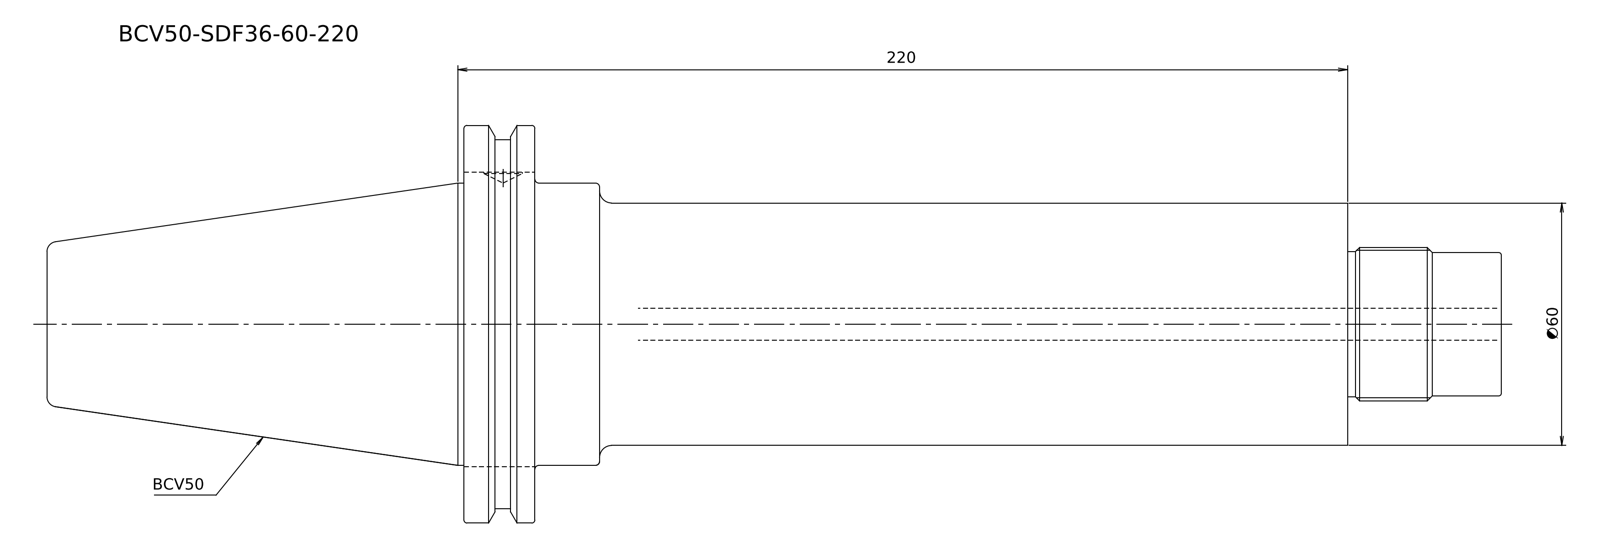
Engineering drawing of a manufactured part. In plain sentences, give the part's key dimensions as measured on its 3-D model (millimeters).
Its 3-D file was written by "Kubotek KeyCreator 2011 V10.0.2 (22737) (automotive_design)". It is 1 solid with 17 faces: 7 planar, 6 cylindrical and 4 other. Overall it measures 321.6 by 98.42 by 98.42 millimeters. Its volume is 966 480 cubic millimeters and its surface area 75 523 square millimeters. Round bosses or shafts: 1 of diameter 98.42, 1 of diameter 91.29, 1 of diameter 69.85, 1 of diameter 60. The main face-to-face distances are 17.55, 200.95, 218.5, 321.6, 120.65, 103.1, 184.95, 16, 33.55, 136.65.
